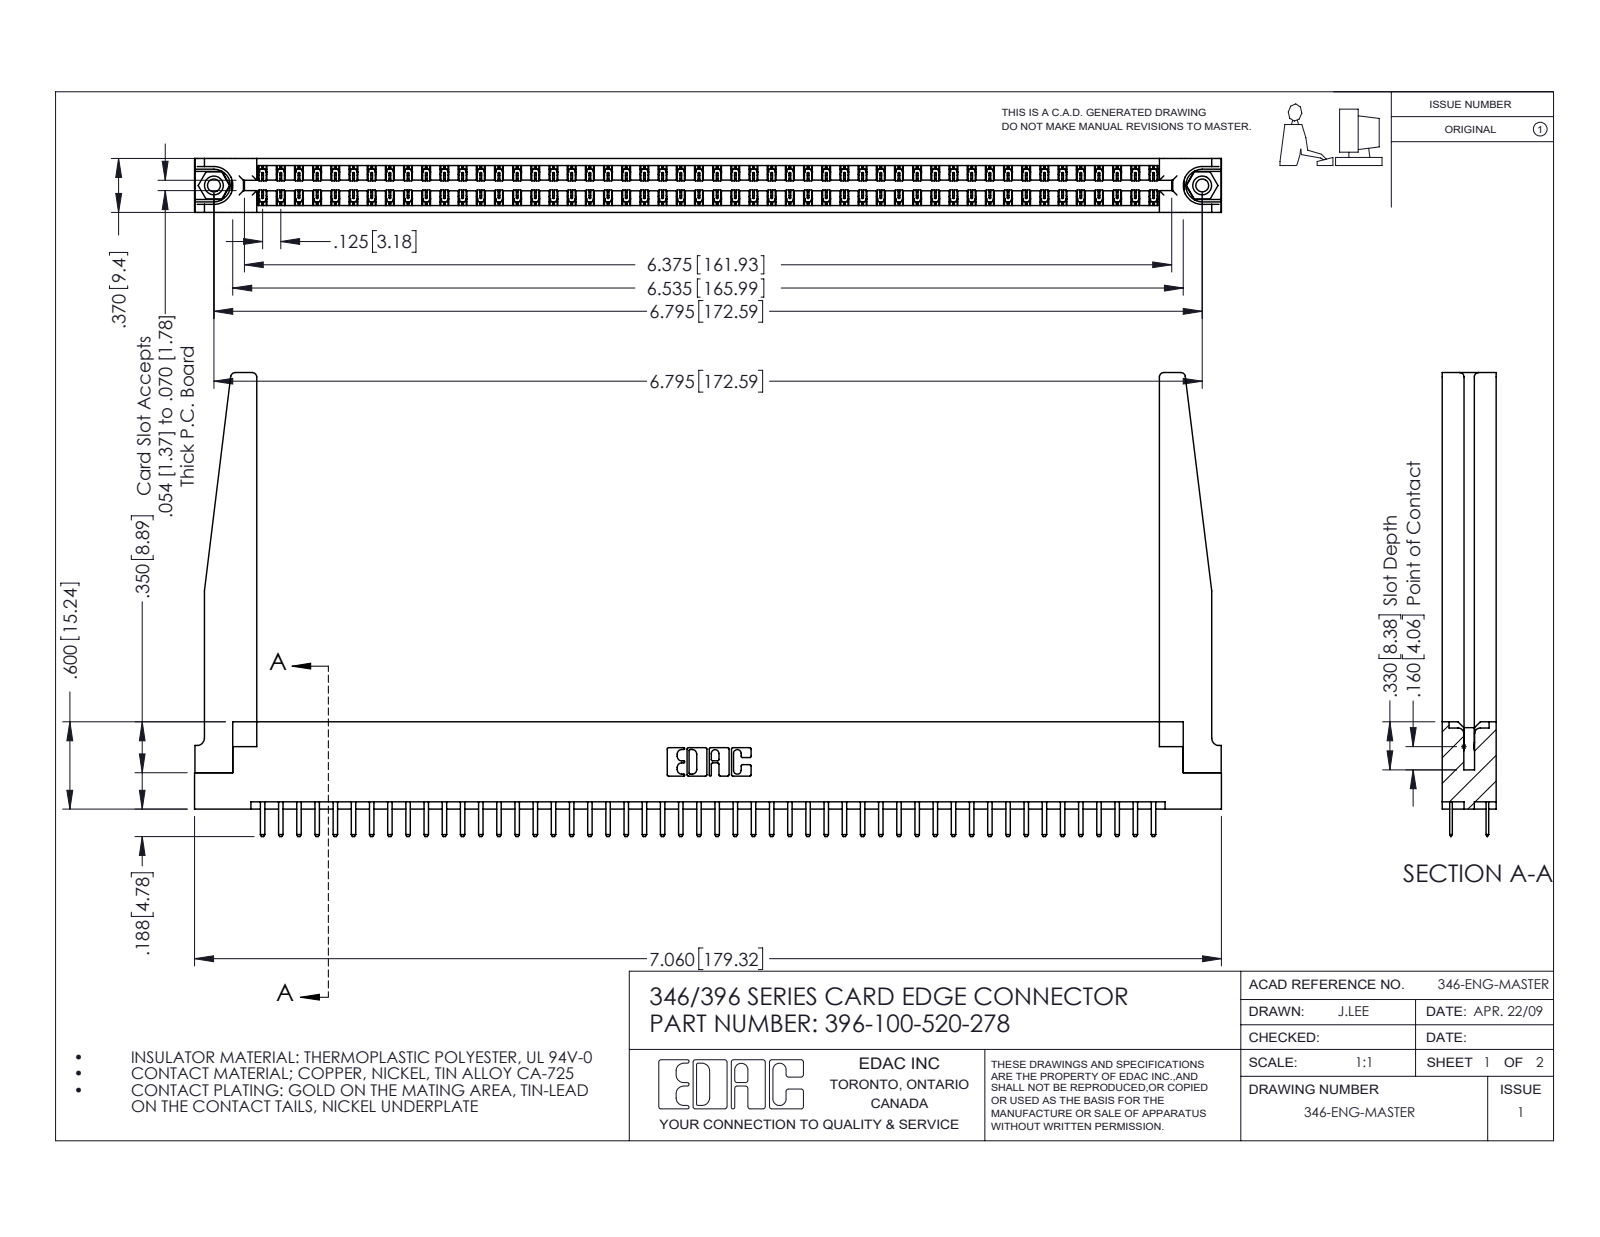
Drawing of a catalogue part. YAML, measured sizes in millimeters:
part_name: "396-100-520-278; 346-220-078_345-220-078; 345-250-001_345-250-001-102; 345-292-001_345-293-120 (+1 more)"
step_written_by: "SolidWorks 2016 (CONFIG_CONTROL_DESIGN)"
units: millimeters
bodies: {solids: 105, faces: 5956, planar: 3918, cylindrical: 1986, other: 52}
overall_size: [179.3, 81, 9.4]
volume: 24420
surface_area: 30620
round_holes:
  - {diameter: 2.3, count: 2}
  - {diameter: 3.2, count: 2}
  - {diameter: 4, count: 2}
  - {diameter: 1.6, count: 1}
round_bosses_or_shafts:
  - {diameter: 3.9, count: 2}
partial_cylinders:
  - {radius: 0.2, count: 150}
  - {radius: 0.3, count: 104}
  - {radius: 0.3, count: 22}
  - {radius: 0.8, count: 8}
  - {radius: 0.2, count: 6}
  - {radius: 0.8, count: 6}
  - {radius: 0.7, count: 3}
  - {radius: 0.4, count: 2}
face_to_face_distances: [9.4, 1.2, 8.2, 6.4, 1.8, 3.8, 3.8, 7.6, 0.6, 7]
hole_center_spacings: [6.2, 167.3, 172.6]
